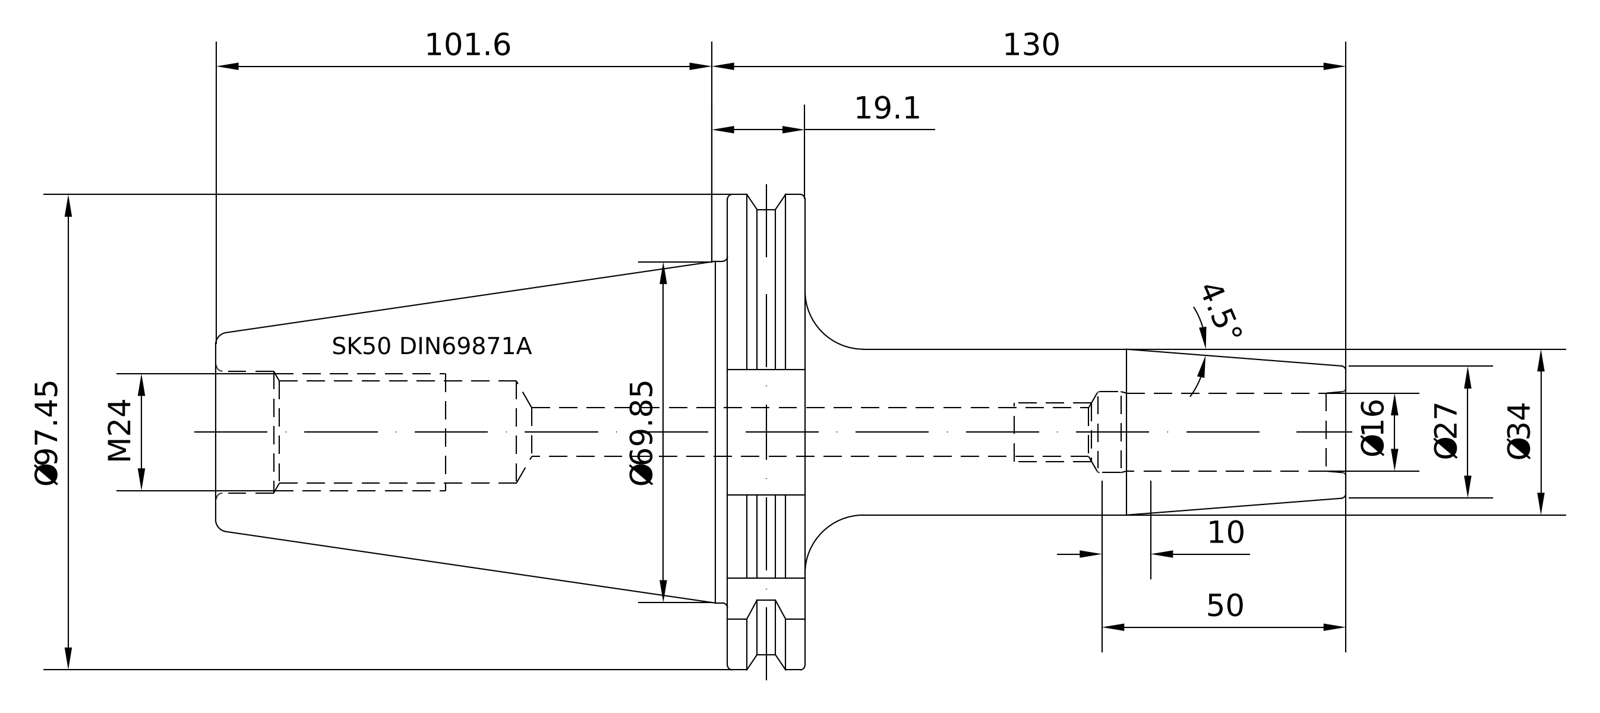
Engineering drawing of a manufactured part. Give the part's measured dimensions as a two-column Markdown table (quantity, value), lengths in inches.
| quantity | value |
| --- | --- |
| part name | 50-444-16 |
| STEP written by | PRO/ENGINEER BY PARAMETRIC TECHNOLOGY CORPORATION, 2010430 (CONFIG_CONTROL_DESIGN) |
| units | inches |
| bodies | 1 solid, 93 faces (21 planar, 24 cylindrical, 48 other) |
| overall size | 9.118 × 3.837 × 3.701 |
| volume | 26 in³ |
| surface area | 86.3 in² |
| round holes (diameter × count) | 0.63 × 1, 0.817 × 1, 0.985 × 1, 1.012 × 1 |
| round bosses / shafts (diameter × count) | 3.583 × 1, 2.722 × 1, 1.339 × 1, 0.945 × 1 |
| partial cylindrical surfaces (radius × count) | 0.069 × 1, 1.919 × 1 |
| main face-to-face distances | 0.624, 2.866, 4.126, 4.75, 1.016, 9.118, 4.992, 4.368, 7.15, 3.024 |
